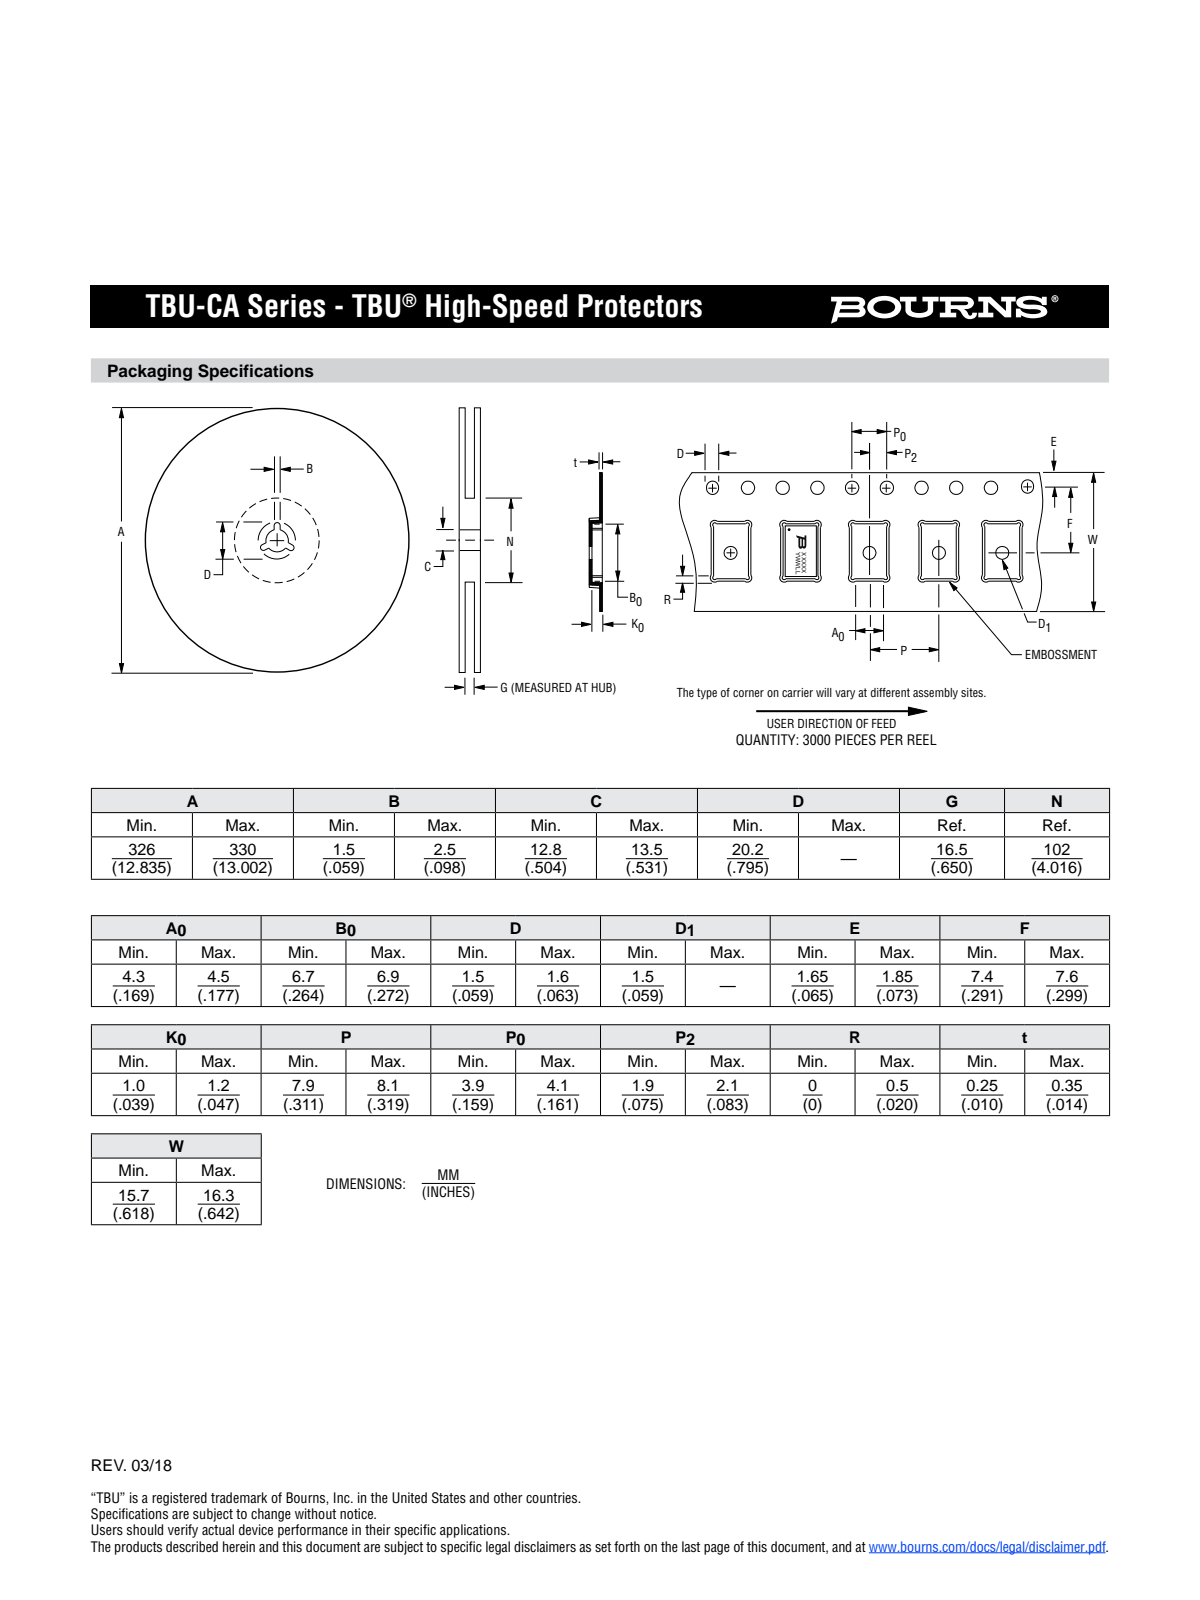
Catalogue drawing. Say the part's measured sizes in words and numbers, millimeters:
The part is named "TBU-CA". Its 3-D file was written by "SolidWorks 2021 (AUTOMOTIVE_DESIGN)". It is 1 solid with 169 faces: 157 planar, 0 cylindrical and 12 other. Overall it measures 6.5 by 4 by 0.88 millimeters. Its volume is 22 cubic millimeters and its surface area 71 square millimeters. The main face-to-face distances are 0.88, 0.85, 4, 6.5, 3.7, 2.15, 2.85, 3.65, 4.35, 0.7.
